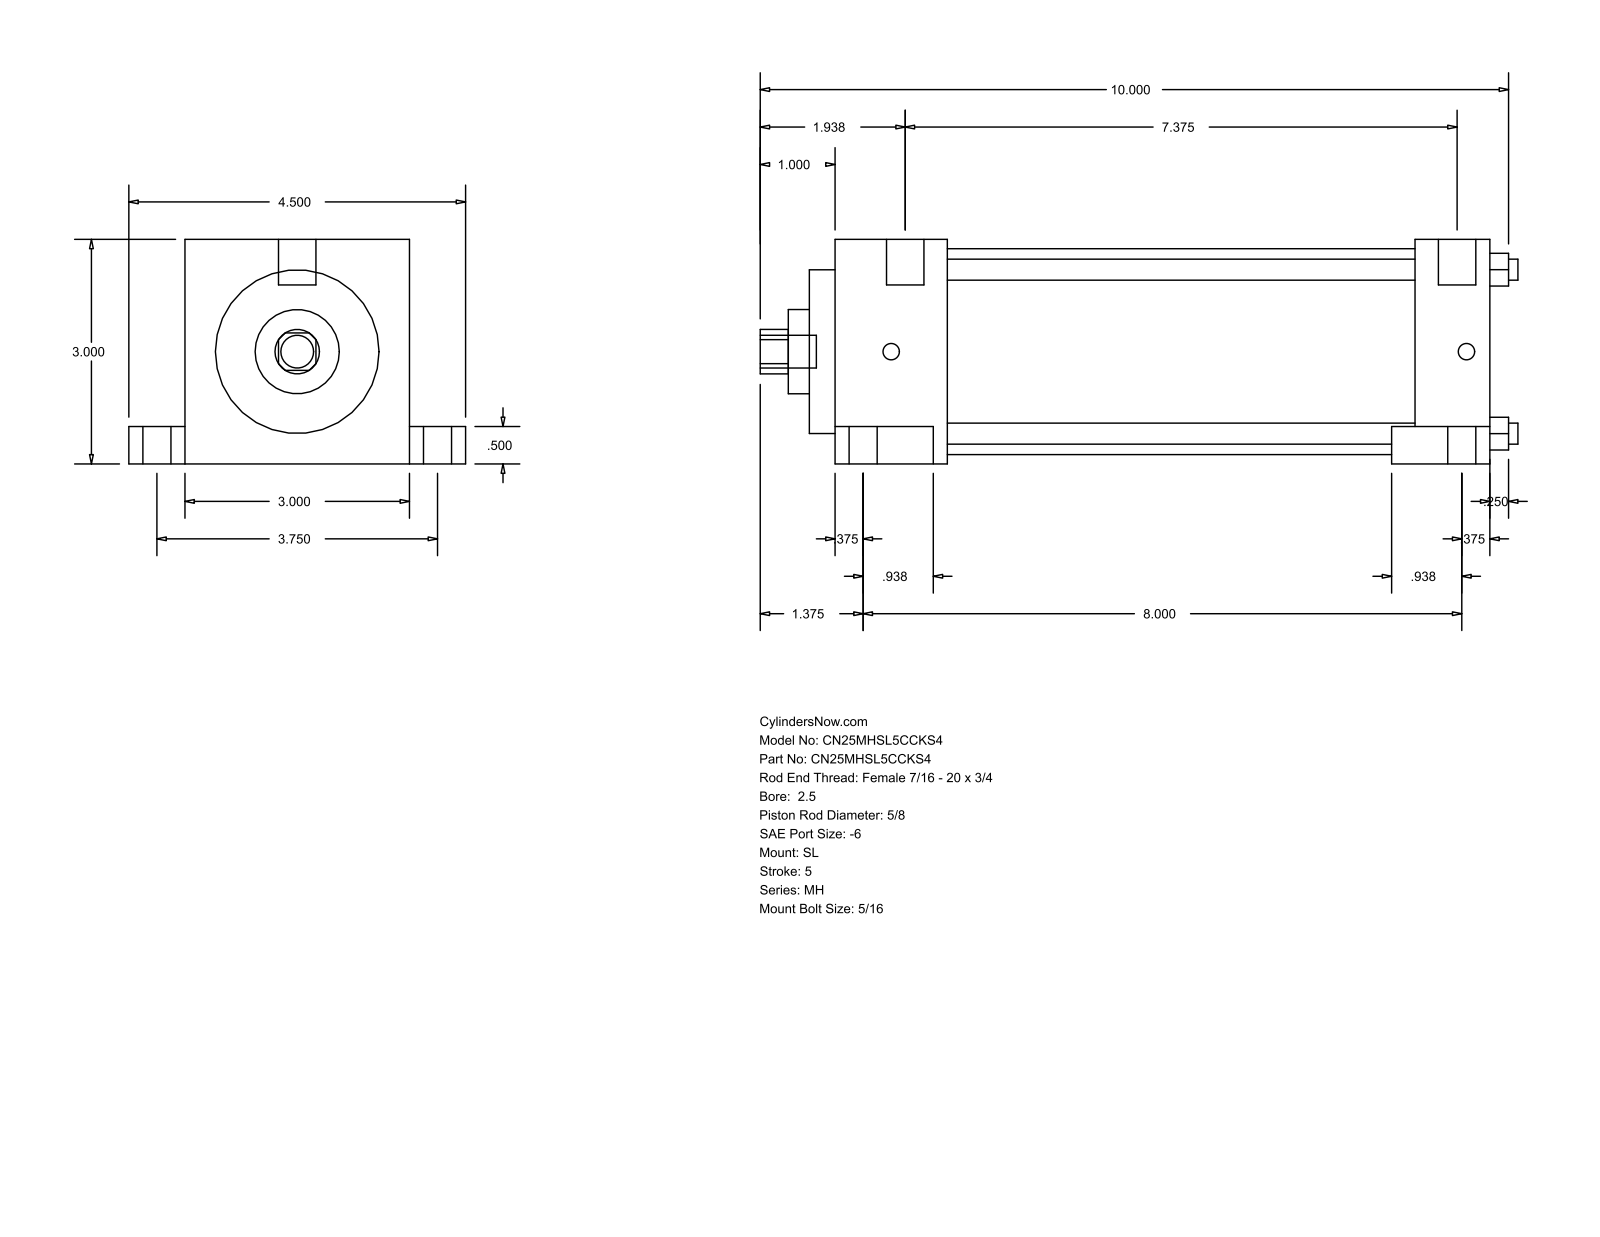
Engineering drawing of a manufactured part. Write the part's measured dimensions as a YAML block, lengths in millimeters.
part_name: "MH_SL__0250_0.625"
step_written_by: "GSSL Pune (CONFIG_CONTROL_DESIGN)"
units: millimeters
bodies: {solids: 0, faces: 86, planar: 61, cylindrical: 25, other: 0}
overall_size: [257.18, 114.3, 76.2]
round_holes:
  - {diameter: 7.14, count: 4}
  - {diameter: 15.88, count: 1}
  - {diameter: 28.57, count: 1}
  - {diameter: 55.55, count: 1}
  - {diameter: 69.85, count: 1}
round_bosses_or_shafts:
  - {diameter: 15.88, count: 2}
  - {diameter: 9.53, count: 2}
  - {diameter: 5.56, count: 2}
  - {diameter: 12.7, count: 1}
  - {diameter: 11.11, count: 1}
partial_cylinders:
  - {radius: 7.54, count: 1}
face_to_face_distances: [76.2, 25.4, 205.58, 230.98, 12.7, 63.5, 19.05, 95.25, 31.75, 197.64]
hole_center_spacings: [39.33, 55.62, 78.66]
